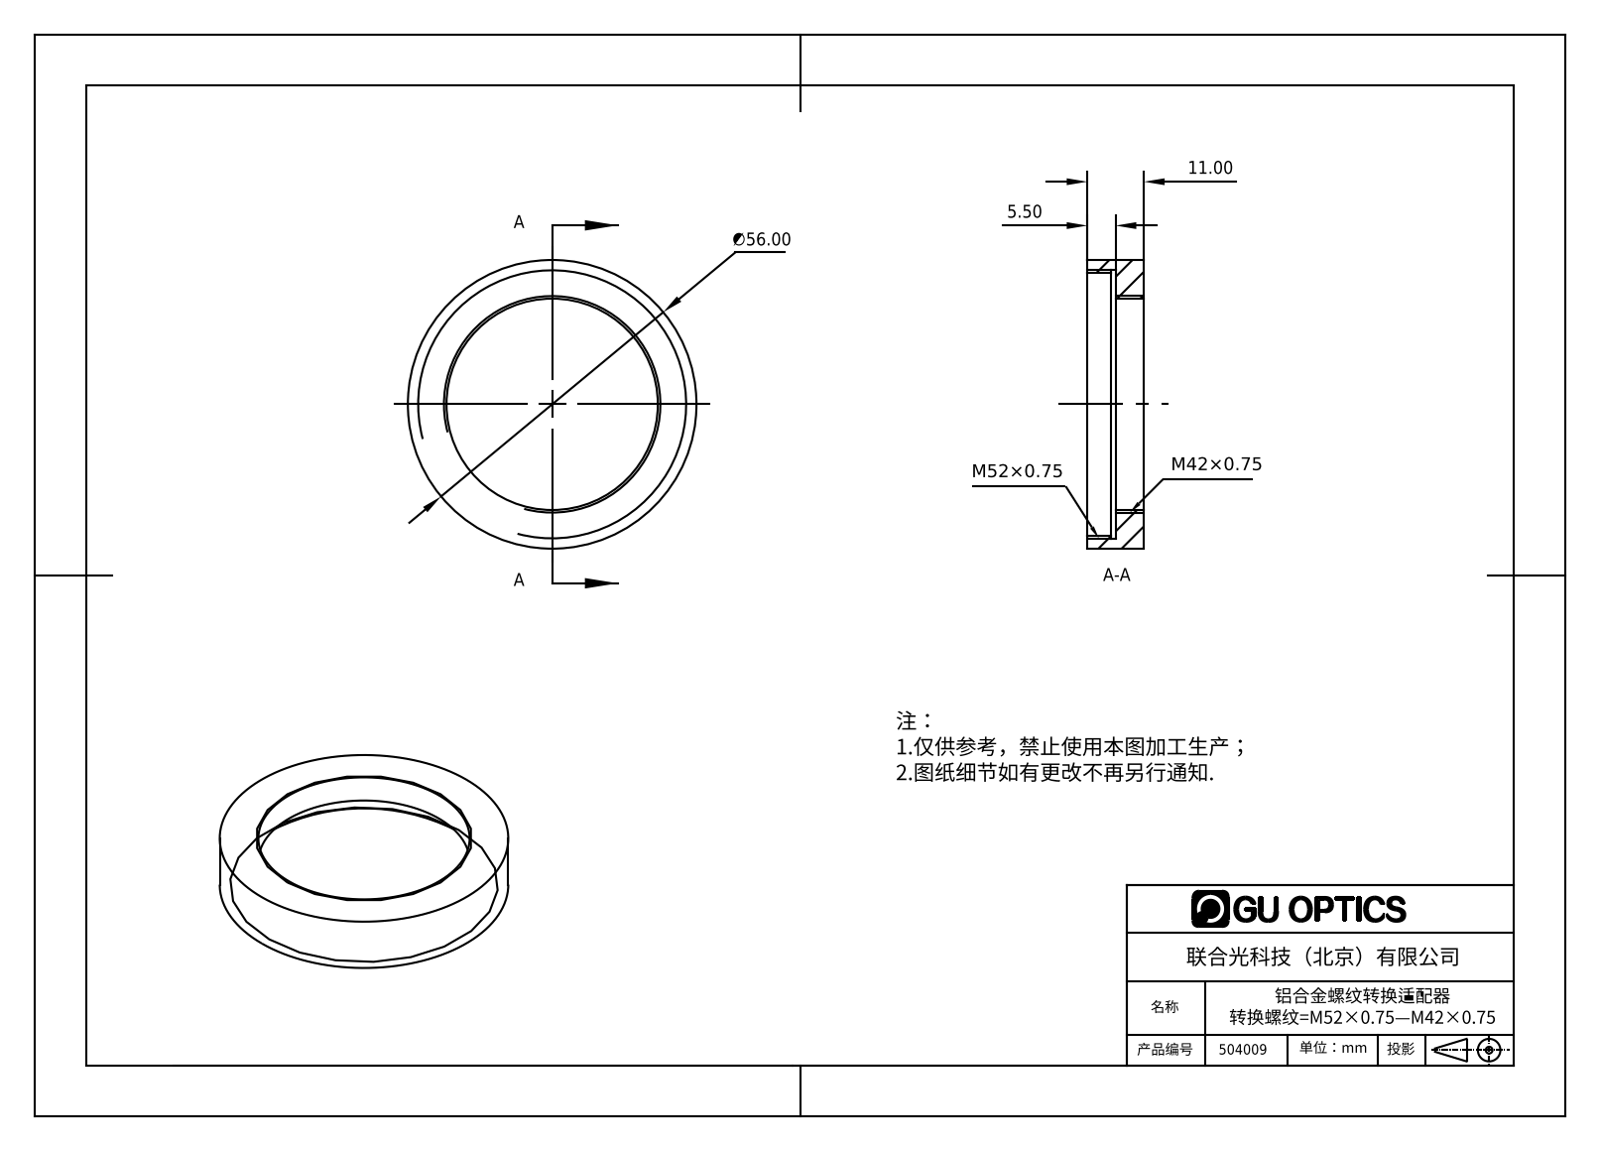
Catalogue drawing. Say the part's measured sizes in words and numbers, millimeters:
The part is named "504009". Its 3-D file was written by "SolidWorks 2016 (AUTOMOTIVE_DESIGN)". It is 1 solid with 12 faces: 4 planar, 8 cylindrical and 0 other. Overall it measures 56 by 56 by 11 millimeters. Its volume is 8 499 cubic millimeters and its surface area 6 009 square millimeters. Round holes: 1 of diameter 41, 1 of diameter 51, 1 of diameter 52.2. Round bosses or shafts: 1 of diameter 56. The main face-to-face distances are 5.5, 11, 4.5, 1, 6.5.
